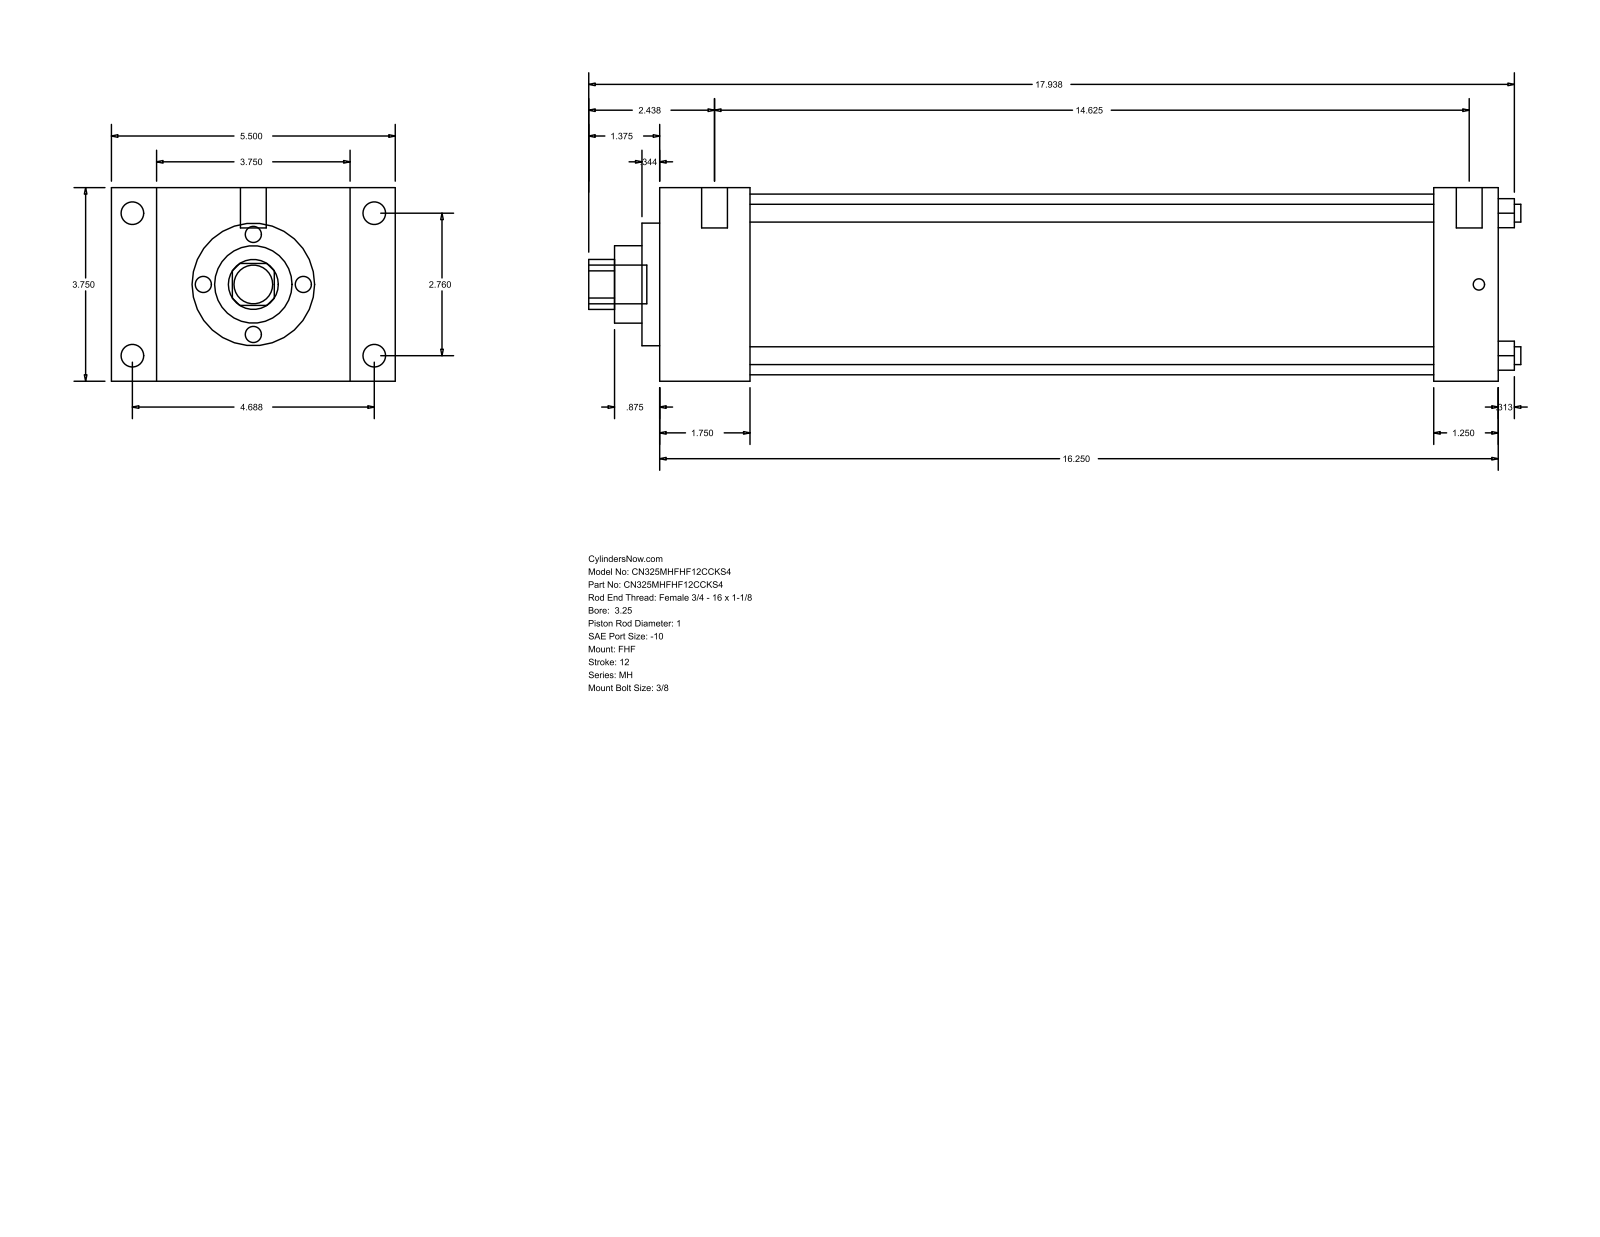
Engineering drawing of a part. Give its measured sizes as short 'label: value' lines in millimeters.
name: MH_FHF__0325_1
written by: GSSL Pune (CONFIG_CONTROL_DESIGN)
unit: mm
bodies: 0 solids, 90 faces (61 planar, 29 cylindrical, 0 other)
size: 458.79 × 139.7 × 95.25
holes: 4× ⌀8.76, 1× ⌀25.4, 1× ⌀38.1, 1× ⌀60.33, 1× ⌀88.9
bosses: 4× ⌀11.13, 4× ⌀5.56, 2× ⌀12.7, 1× ⌀19.05
rounds: 1× R12.29
face distances: 95.24, 412.76, 44.46, 368.3, 22.23, 117.47, 139.7, 381.01, 336.55, 31.75
hole spacings: 49.57, 70.1, 99.14
